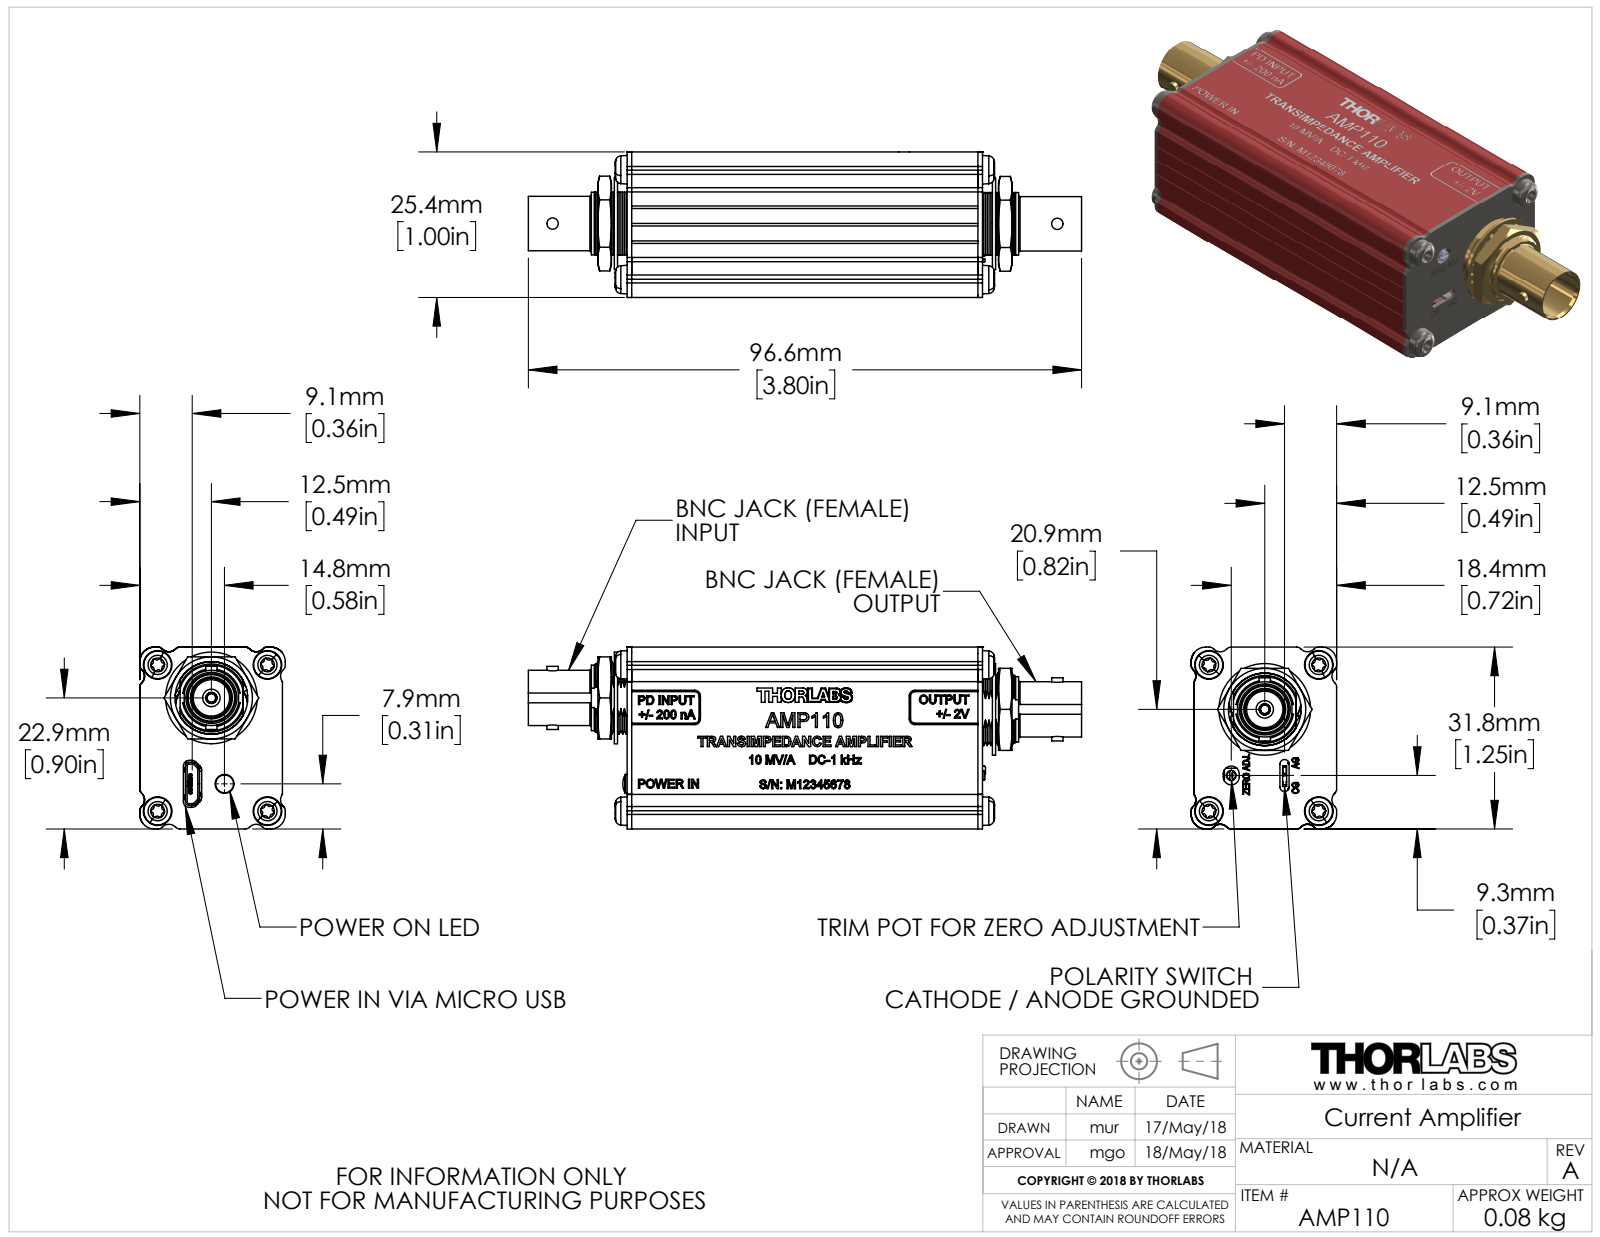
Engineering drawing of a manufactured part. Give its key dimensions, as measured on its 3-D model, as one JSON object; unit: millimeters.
{"part_name": "AMP110 WEB", "step_written_by": "SolidWorks 2018 (CONFIG_CONTROL_DESIGN)", "units": "millimeters", "bodies": {"solids": 22, "faces": 4939, "planar": 2649, "cylindrical": 1033, "other": 1257}, "overall_size": [96.6, 31.75, 25.4], "volume_mm3": 23401, "surface_area_mm2": 26751, "round_holes": [[3.5, 8], [0.6, 4], [1.19, 2], [1.49, 2], [1.93, 2], [4.04, 2], [6.93, 2], [8.86, 2], [12.7, 2], [14, 2], [1.04, 1], [1.24, 1]], "round_bosses_or_shafts": [[0.46, 6], [2.5, 4], [2.22, 4], [16, 2], [11.43, 2], [10.46, 2], [9.65, 2], [6.91, 2]], "partial_cylinders_radius": [[0.24, 48], [0.42, 48], [0.2, 25], [0.15, 20], [1.02, 20], [0.25, 12], [0.25, 11], [1.59, 11]], "face_to_face_distances": [1.27, 3.05, 6.1, 4.32, 9.14, 0.8, 61.26, 12.19, 17.91, 24.89], "hole_center_spacings": [19.18, 2, 11.19, 12.34, 25.53, 31.93, 2.01, 4]}
